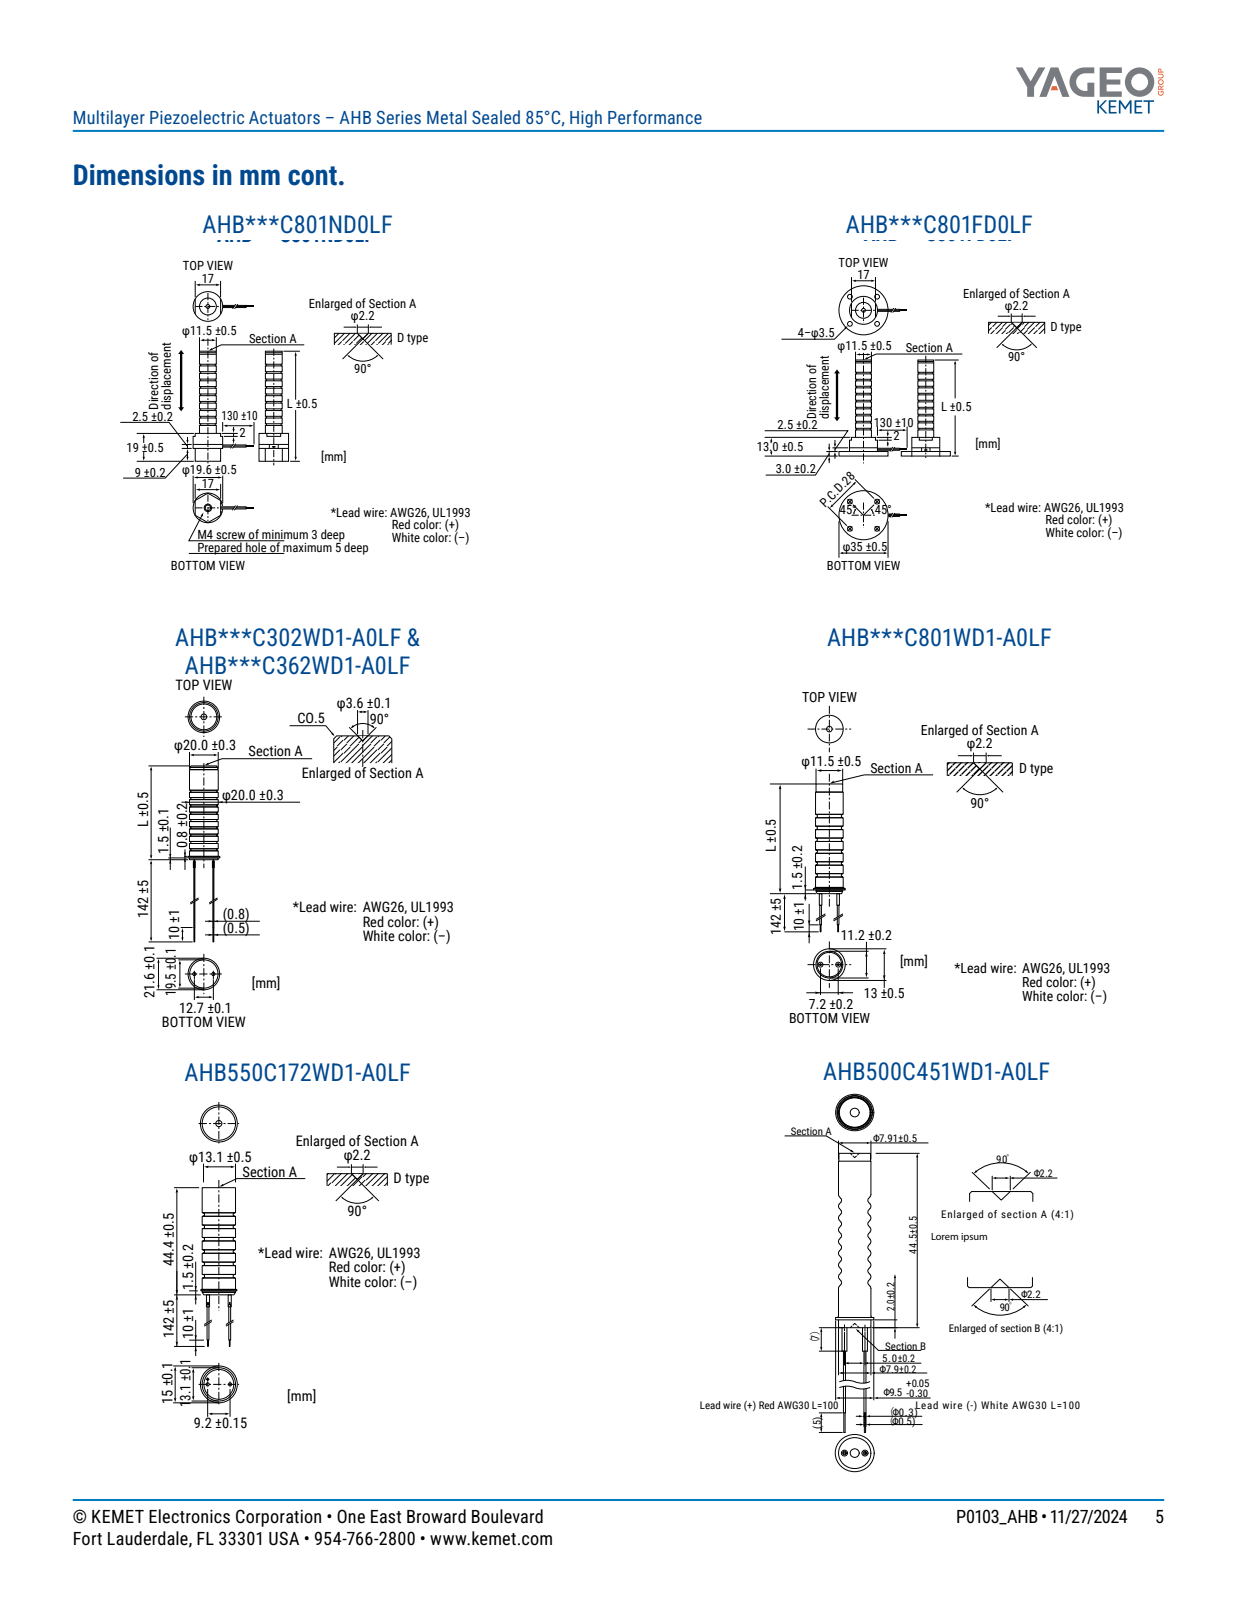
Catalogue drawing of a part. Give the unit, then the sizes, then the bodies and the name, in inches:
Units: inches
Overall size (bounding box): 8.343 × 0.531 × 0.531
Round bosses / shafts (diameter × count): ⌀0.039 ×2, ⌀0.031 ×2, ⌀0.024 ×2, ⌀0.531 ×1, ⌀0.449 ×1
Main face-to-face distances: 0.106, 2.555, 2.449, 0.067, 0.039, 2.488, 2.556, 2.489, 2.449, 5.787
Volume: 0.409 in³ · Surface area: 5.732 in²
Bodies: 2 solids, 131 faces (65 planar, 34 cylindrical, 32 other)
Part name (STEP PRODUCT): AL_KAHB1_D12L64.9
STEP written by: SolidWorks 2014 (AUTOMOTIVE_DESIGN)
